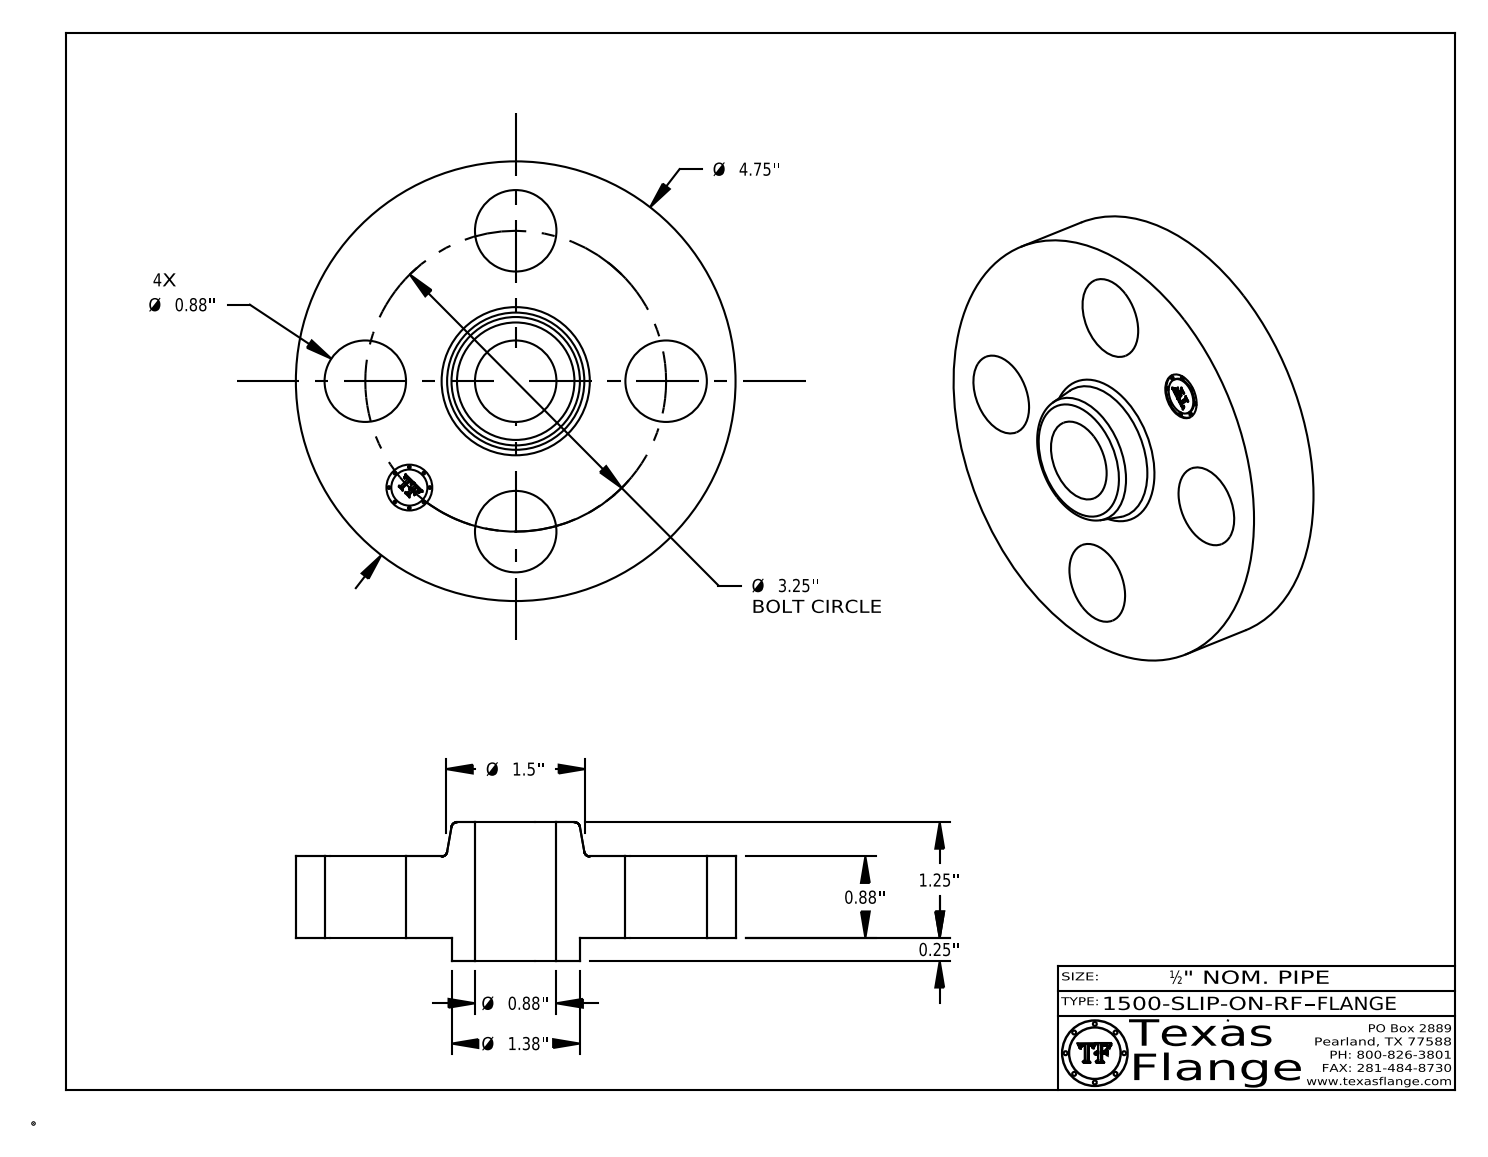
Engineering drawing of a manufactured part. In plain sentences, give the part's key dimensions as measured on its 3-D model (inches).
The part is named "1500-SLIP-ON-RF". Its 3-D file was written by "CATIA V5 STEP AP214 (AUTOMOTIVE_DESIGN)". It is 1 solid with 409 faces: 369 planar, 34 cylindrical and 6 other. Overall it measures 4.75 by 4.75 by 1.5 inches. Its volume is 13.51 cubic inches and its surface area 58.79 square inches. Round holes: 5 of diameter 0.88, 1 of diameter 0.495. Round bosses or shafts: 8 of diameter 0.03, 1 of diameter 4.75, 1 of diameter 1.38, 1 of diameter 0.39. The main face-to-face distances are 0.88, 0.25, 1.13, 1.5, 1.25, 0.37, 1.115, 0.865, 0.015, 0.385. The hole center spacings are 1.625, 2.298, 1.244, 3.003, 3.25.
